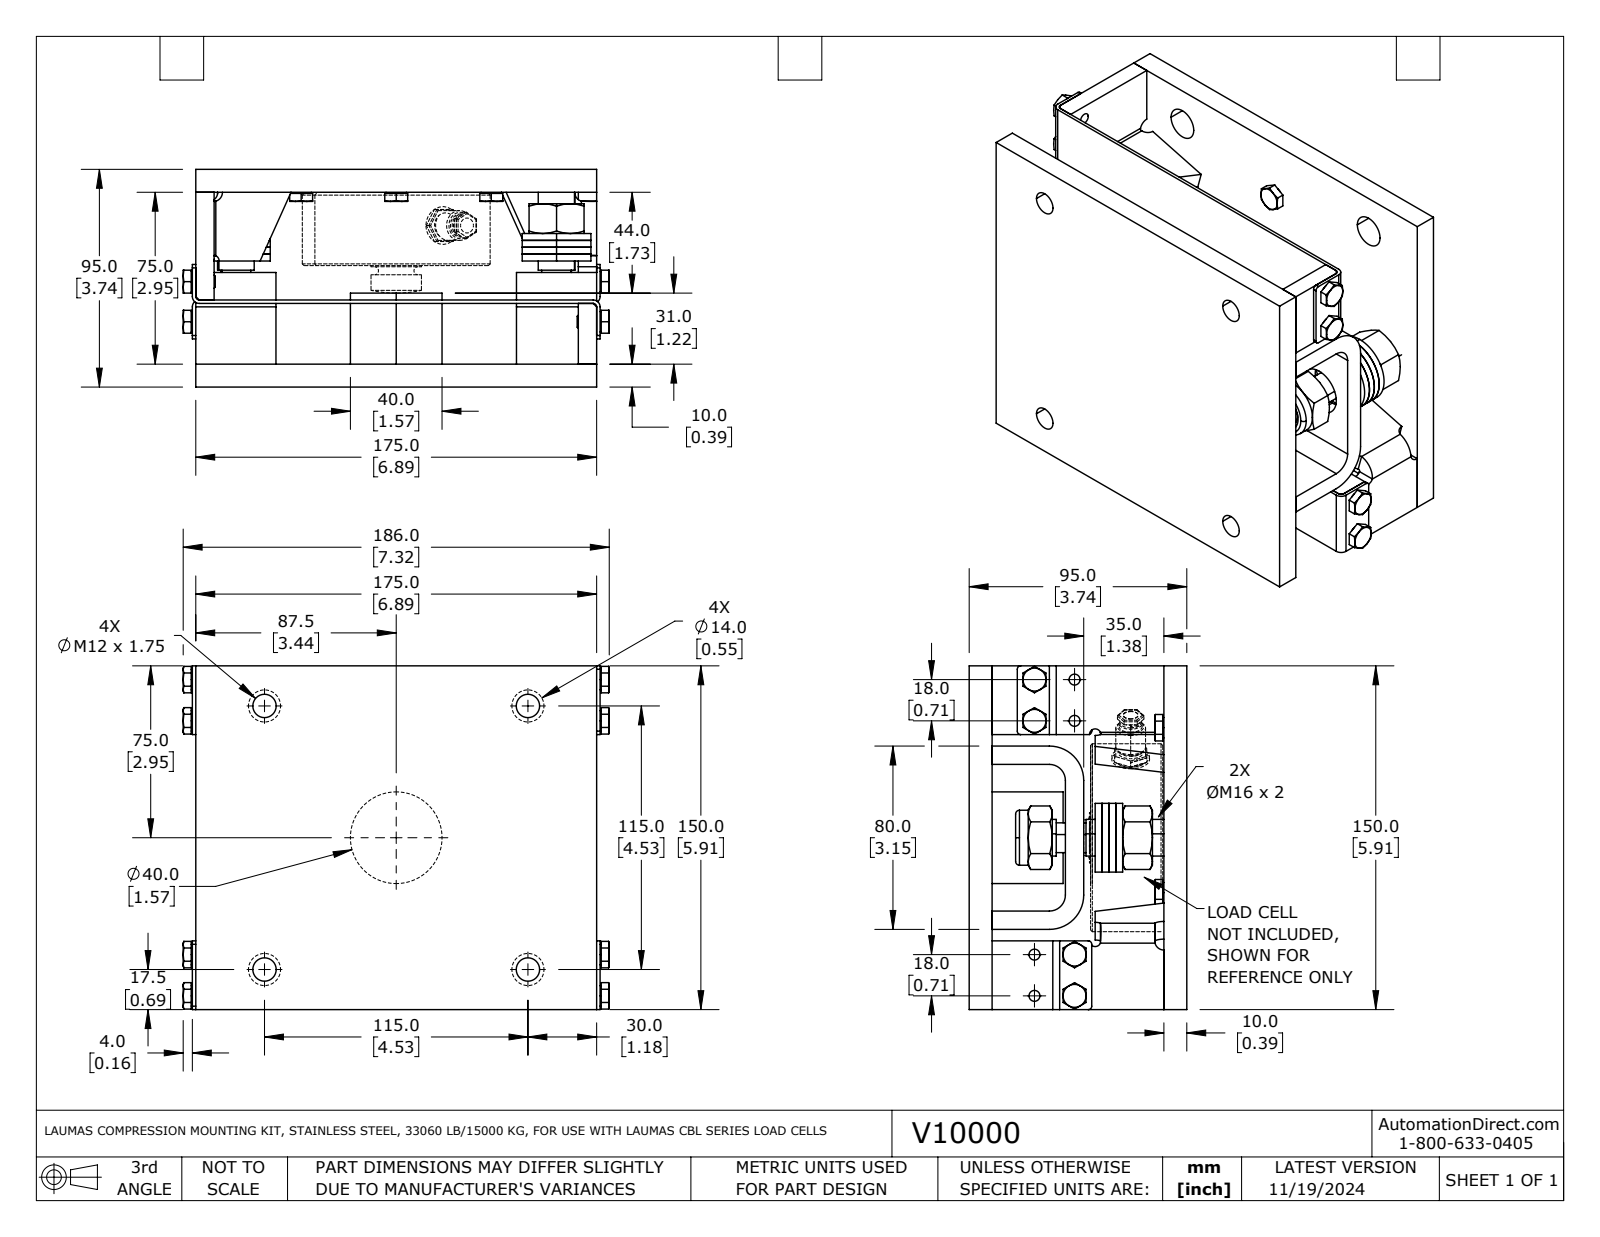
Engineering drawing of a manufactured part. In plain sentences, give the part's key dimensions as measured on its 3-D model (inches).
The part is named "V10000". Its 3-D file was written by "SolidWorks 2021 (AUTOMOTIVE_DESIGN)". It is 36 solids with 716 faces: 262 planar, 257 cylindrical and 197 other. Overall it measures 7.323 by 5.906 by 3.74 inches. Its volume is 45.8 cubic inches and its surface area 354.4 square inches. Round holes: 11 of diameter 0.197, 8 of diameter 0.295, 6 of diameter 0.551, 4 of diameter 0.402, 2 of diameter 0.545, 2 of diameter 0.669, 2 of diameter 0.681, 2 of diameter 0.827. Round bosses or shafts: 11 of diameter 0.35, 11 of diameter 0.236, 2 of diameter 1.181, 2 of diameter 0.945, 2 of diameter 0.63, 2 of diameter 0.512, 1 of diameter 1.575. Partial cylindrical surfaces (rounded edges, fillets, slot ends): 12 of radius 0.059, 4 of radius 0.098, 4 of radius 0.118, 4 of radius 0.157, 2 of radius 0.039, 2 of radius 0.276, 2 of radius 0.354, 2 of radius 0.591. The main face-to-face distances are 3.346, 0.394, 2.953, 3.74, 0.315, 2.244, 1.102, 0.059, 1.437, 1.496. The hole center spacings are 0.689, 0.709, 0.988, 2.317, 4.528, 4.724, 4.774, 5.507.
